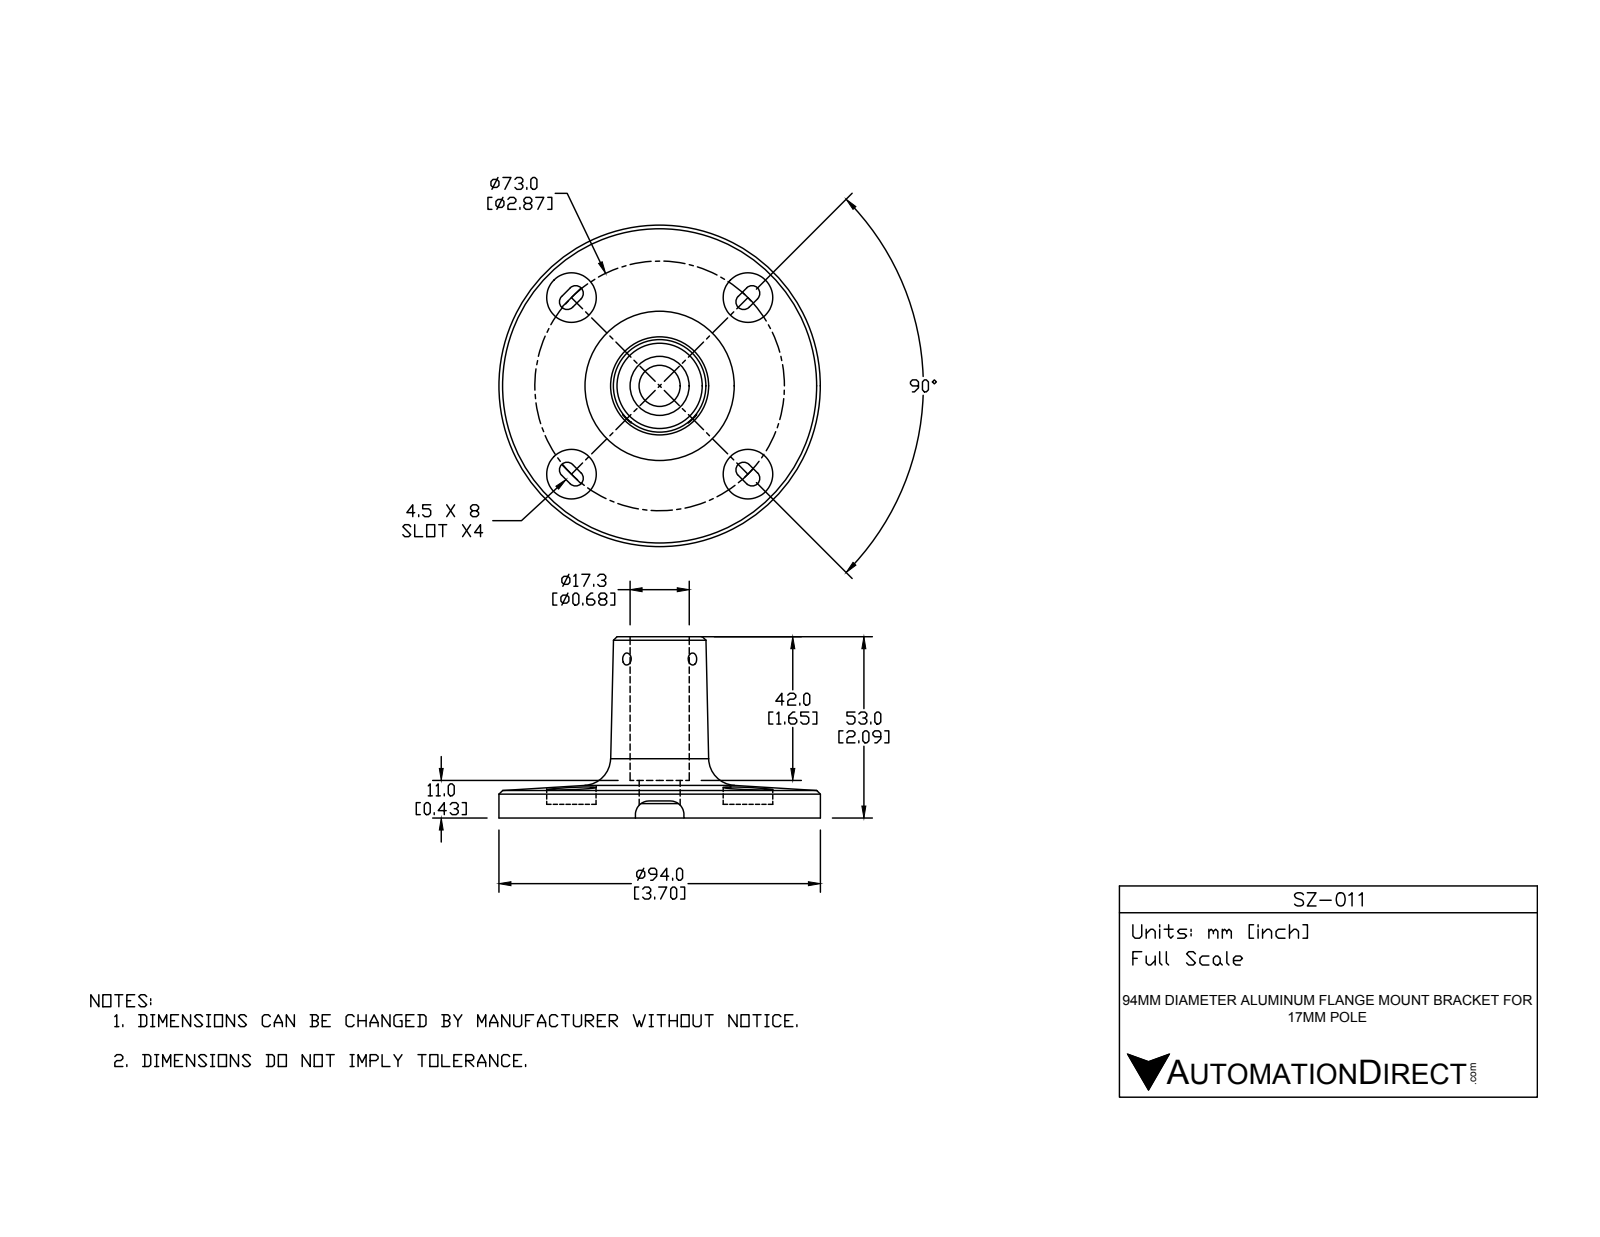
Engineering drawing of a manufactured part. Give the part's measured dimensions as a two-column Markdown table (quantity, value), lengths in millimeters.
| quantity | value |
| --- | --- |
| part name | SZ-011 |
| STEP written by | SolidWorks 2016 (AUTOMOTIVE_DESIGN) |
| units | millimeters |
| bodies | 1 solid, 112 faces (34 planar, 57 cylindrical, 21 other) |
| overall size | 94 × 94 × 53 |
| volume | 36 640 mm³ |
| surface area | 24 974 mm² |
| round holes (diameter × count) | 14.5 × 4, 3.5 × 2, 12 × 1, 17.3 × 1, 90 × 1 |
| round bosses / shafts (diameter × count) | 18.5 × 4, 94 × 1 |
| partial cylindrical surfaces (radius × count) | 2.25 × 8, 4.25 × 8, 4 × 2 |
| main face-to-face distances | 2, 4, 53, 51, 49, 11, 9, 7, 42, 36.49 |
| hole center spacings | 36.5, 51.62, 73 |
